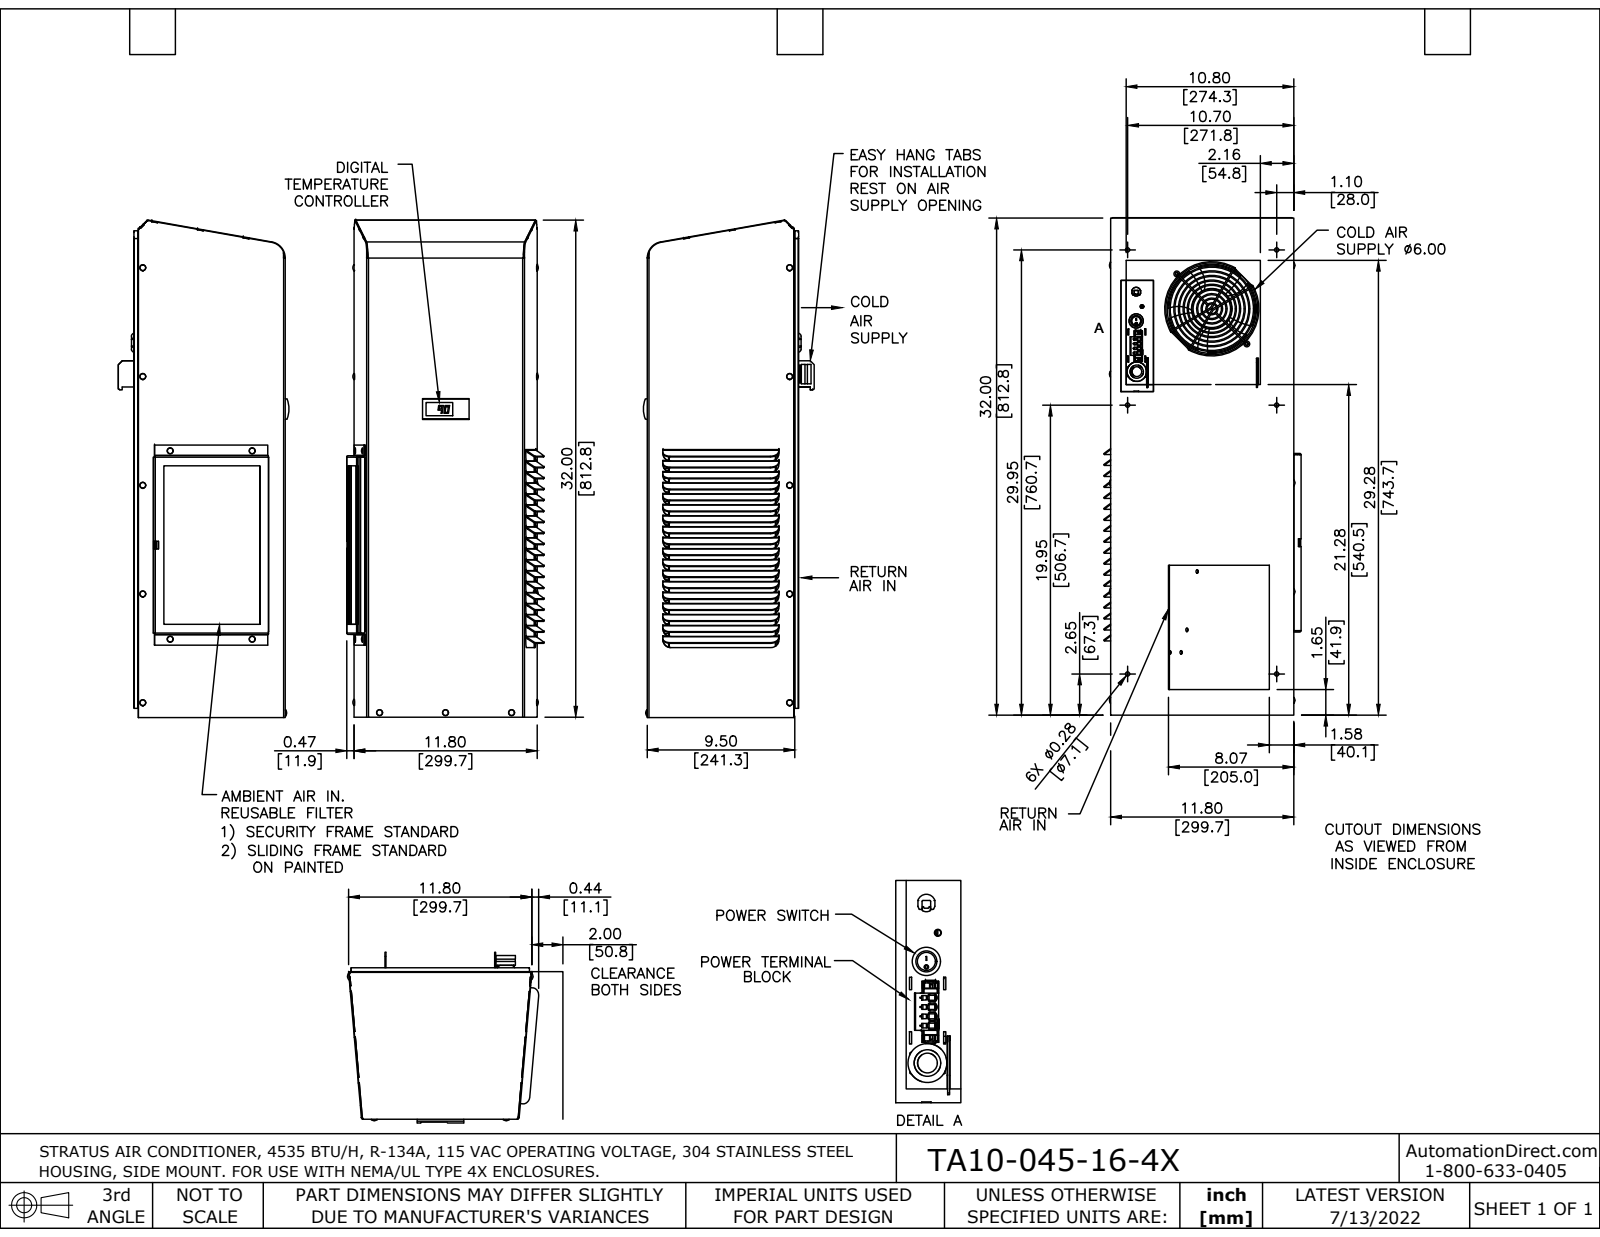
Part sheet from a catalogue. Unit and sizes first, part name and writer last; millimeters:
Units: millimetres
Overall size (bounding box): 813.4 × 319.4 × 293.3
Round holes (diameter × count): ⌀4 ×11, ⌀5.2 ×5, ⌀152.4 ×1
Round bosses / shafts (diameter × count): ⌀4.8 ×7, ⌀9.6 ×2, ⌀9 ×2, ⌀6.3 ×2, ⌀154.2 ×1, ⌀23 ×1, ⌀2.2 ×1
Partial cylindrical surfaces — rounded edges, fillets, slot ends (radius × count): R0.4 ×45, R0.3 ×42, R12.7 ×36, R12.9 ×36, R2.5 ×28, R1.5 ×21, R2.9 ×21, R0.8 ×13
Main face-to-face distances: 1.5, 239.6, 238.2, 1.5, 241.1, 2.3, 6.4, 7.8, 246, 247.5
Hole centre spacings: 177.8, 355.6, 533.4, 44, 134.6, 166.8, 276.1, 307.8
Volume: 2 237 000 mm³ · Surface area: 2 063 000 mm²
Bodies: 1 solid, 1744 faces (1077 planar, 497 cylindrical, 170 other)
Part name (STEP PRODUCT): TA10-045-16-4X
STEP written by: SolidWorks 2021 (AUTOMOTIVE_DESIGN)
